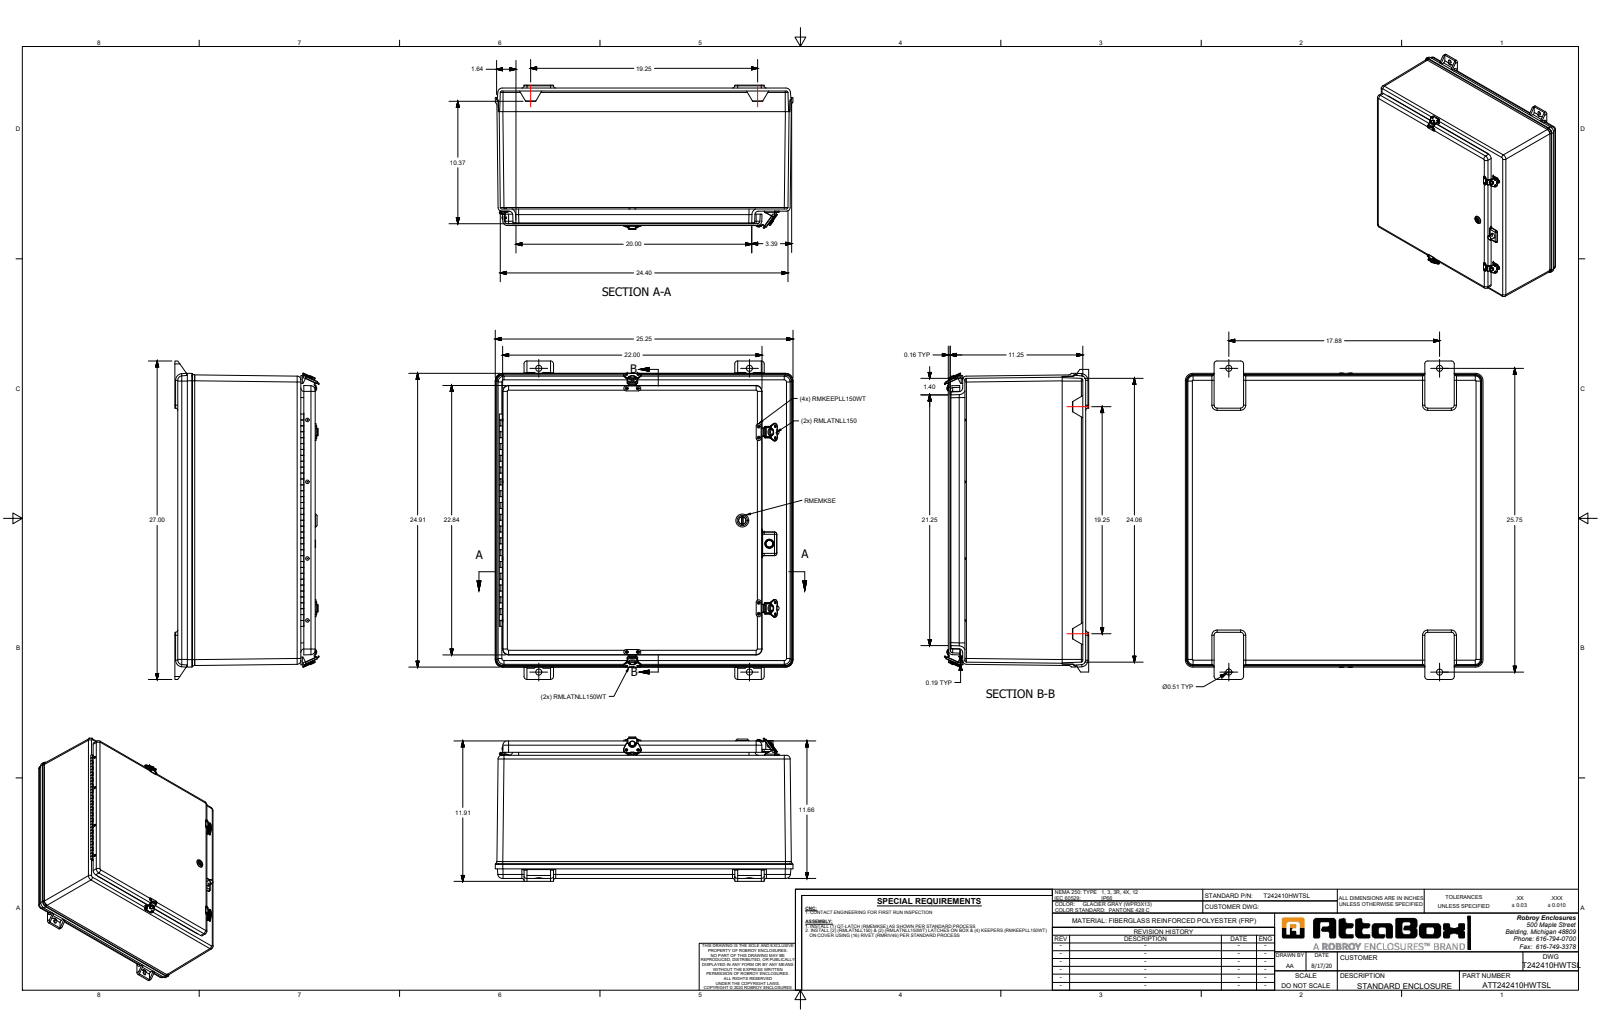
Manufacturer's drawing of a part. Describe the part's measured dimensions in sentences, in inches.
The part is named "T242410HWTSL". Its 3-D file was written by "SolidWorks 2019 (AUTOMOTIVE_DESIGN)". It is 62 solids with 1828 faces: 726 planar, 717 cylindrical and 385 other. Overall it measures 27 by 25.25 by 12.24 inches. Its volume is 504.8 cubic inches and its surface area 5 345 square inches. Round holes: 32 of diameter 0.13, 16 of diameter 0.063, 8 of diameter 0.138, 8 of diameter 0.187, 7 of diameter 0.065, 4 of diameter 0.281, 4 of diameter 0.563, 3 of diameter 0.156, 2 of diameter 0.135, 2 of diameter 0.145, 2 of diameter 0.51, 2 of diameter 0.51. Round bosses or shafts: 16 of diameter 0.14, 8 of diameter 0.297, 4 of diameter 0.5, 3 of diameter 0.2, 2 of diameter 0.281, 2 of diameter 0.135, 1 of diameter 1.102, 1 of diameter 0.78. Partial cylindrical surfaces (rounded edges, fillets, slot ends): 101 of radius 0.01, 30 of radius 0.012, 24 of radius 0.25, 16 of radius 0.03, 15 of radius 0.312, 12 of radius 0.02, 12 of radius 0.187, 12 of radius 0.375. The main face-to-face distances are 0.187, 0.25, 0.156, 11.656, 11.406, 11.5, 11.25, 10.437, 10.25, 10. The hole center spacings are 5.25, 11.75, 6.5, 17, 0.736, 1, 1.006, 1.512.
